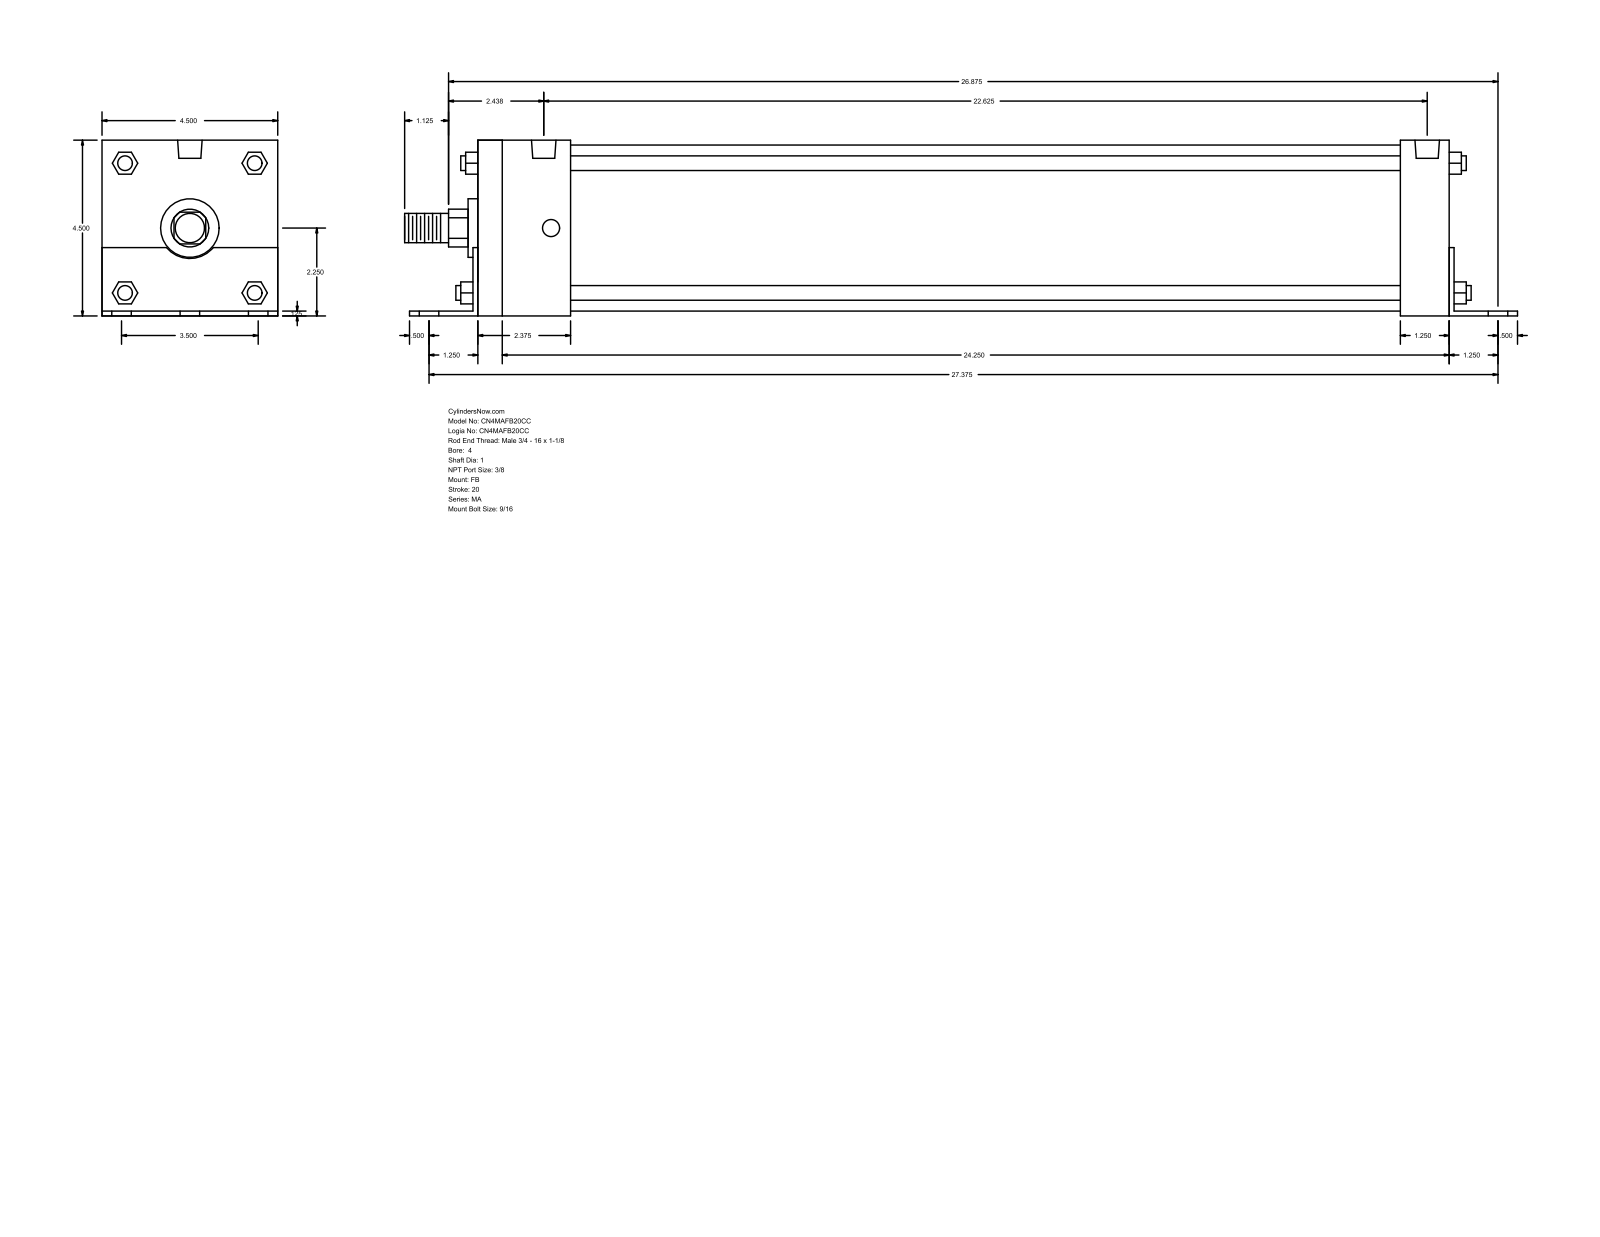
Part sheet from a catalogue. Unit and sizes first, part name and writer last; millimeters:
Units: millimetres
Overall size (bounding box): 723.9 × 114.35 × 114.3
Round holes (diameter × count): ⌀14.29 ×6, ⌀11.11 ×4, ⌀15.93 ×2
Round bosses / shafts (diameter × count): ⌀9.53 ×4, ⌀107.95 ×1, ⌀38.1 ×1, ⌀25.4 ×1, ⌀19.05 ×1
Partial cylindrical surfaces — rounded edges, fillets, slot ends (radius × count): R12.29 ×1, R19.81 ×1
Main face-to-face distances: 114.3, 3.17, 114.35, 635, 3.12, 111.18, 631.83, 638.17, 34.93, 603.24
Hole centre spacings: 44.45, 696.74, 695.32, 4.76, 63.99, 67.49, 86.85, 88.9
Bodies: 0 solids, 140 faces (105 planar, 35 cylindrical, 0 other)
Part name (STEP PRODUCT): MA_FB__0400_1
STEP written by: GSSL Pune (CONFIG_CONTROL_DESIGN)
